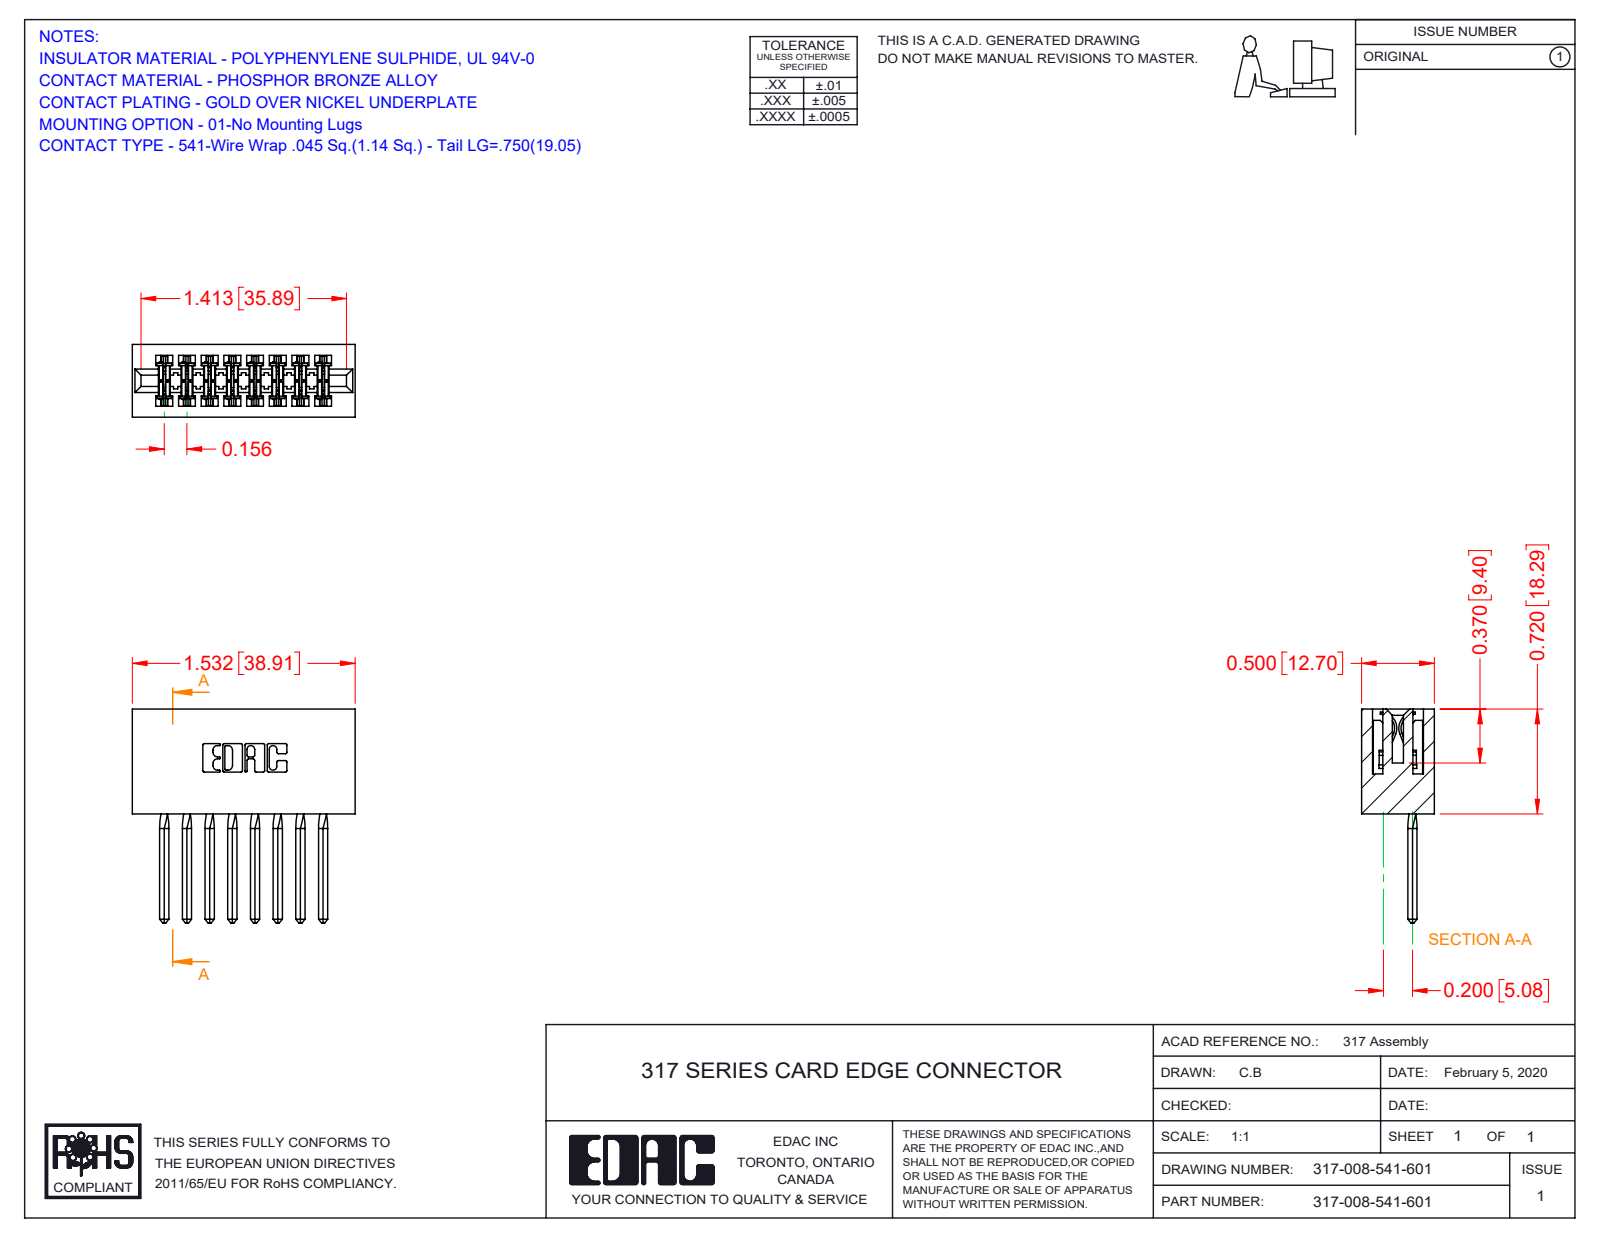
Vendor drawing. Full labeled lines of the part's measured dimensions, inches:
Part name (STEP PRODUCT): 317-008-541-601; 317-290-002_541; 317 Part_Lugless
STEP written by: SolidWorks 2016 (CONFIG_CONTROL_DESIGN)
Units: inches
Bodies: 9 solids, 1306 faces (1042 planar, 232 cylindrical, 32 other)
Overall size (bounding box): 1.532 × 1.47 × 0.5
Volume: 0.425 in³ · Surface area: 13.81 in²
Partial cylindrical surfaces — rounded edges, fillets, slot ends (radius × count): R0.01 ×22, R0.015 ×16, R0.007 ×6, R0.031 ×6, R0.026 ×3, R0.095 ×2, R0.1 ×2, R0.11 ×2
Main face-to-face distances: 0.5, 0.075, 0.425, 0.11, 0.156, 0.065, 0.22, 0.116, 0.624, 0.312
